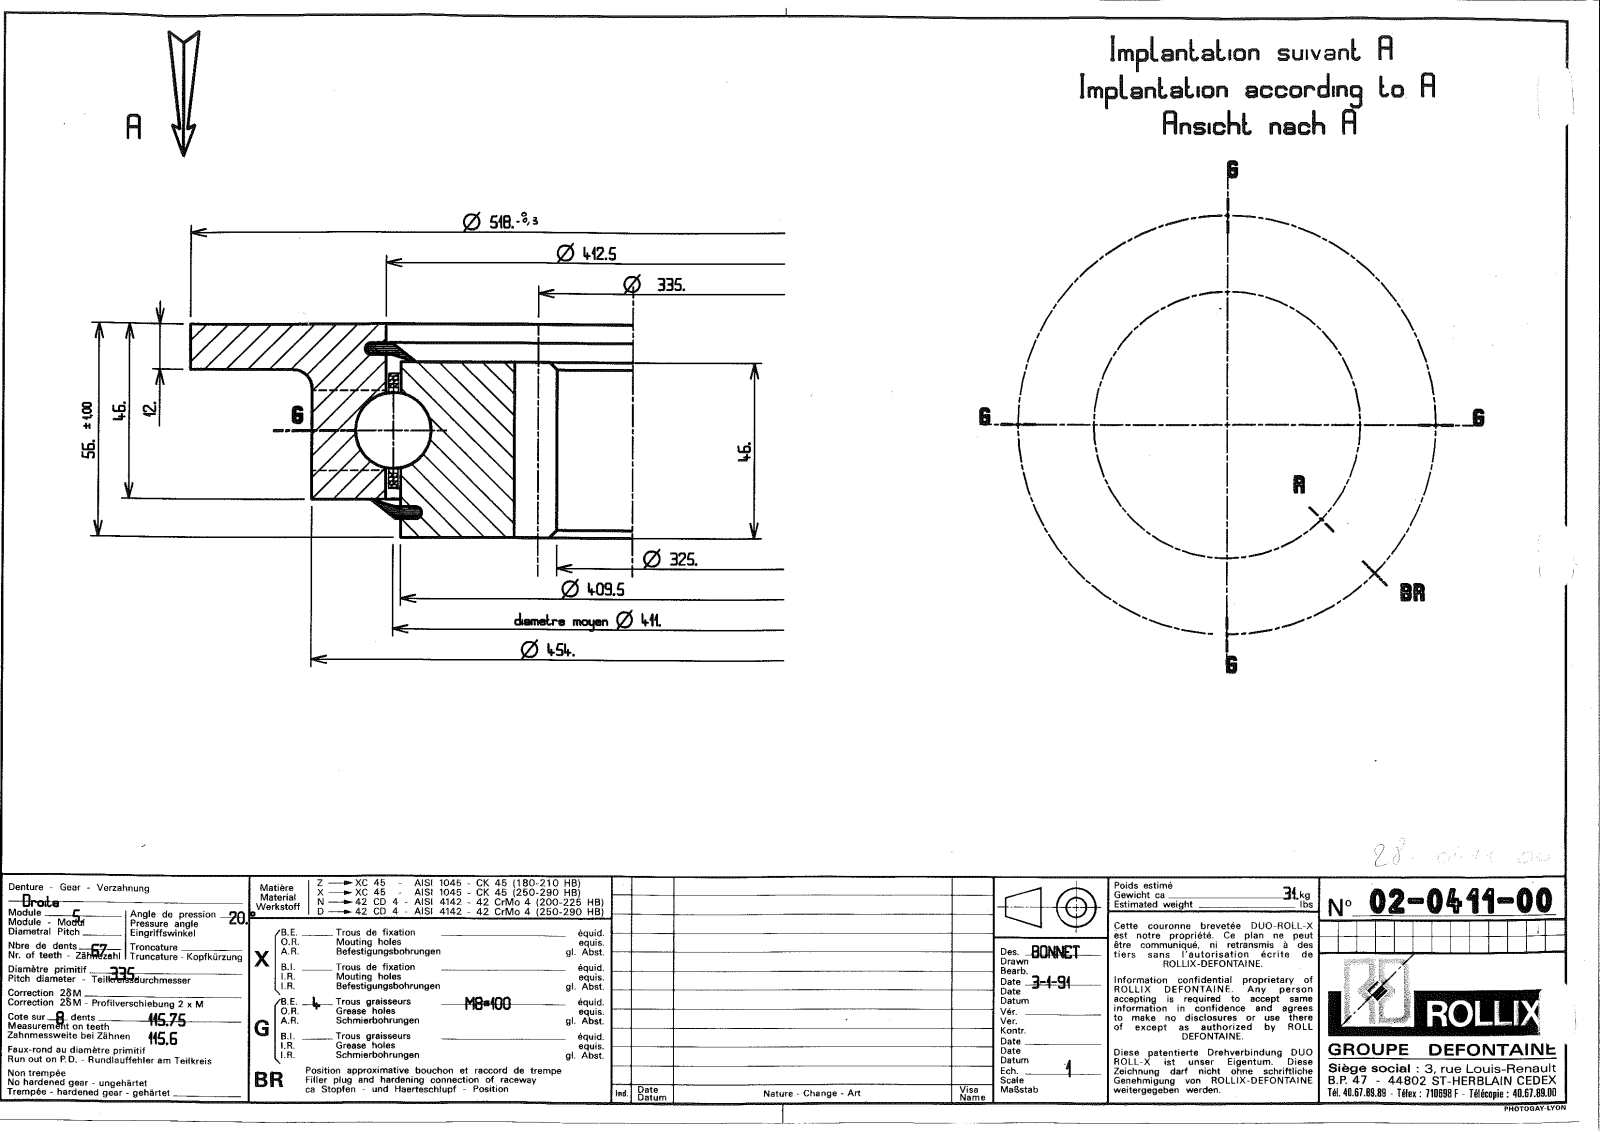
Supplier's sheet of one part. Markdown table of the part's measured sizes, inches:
| quantity | value |
| --- | --- |
| part name | 22-0411-00 |
| STEP written by | SolidWorks 2016 (CONFIG_CONTROL_DESIGN) |
| units | inches |
| bodies | 9 solids, 559 faces (187 planar, 167 cylindrical, 205 other) |
| overall size | 20.394 × 20.394 × 2.205 |
| volume | 211.8 in³ |
| surface area | 981.5 in² |
| round holes (diameter × count) | 0.276 × 4, 16.358 × 1 |
| round bosses / shafts (diameter × count) | 0.315 × 4, 20.394 × 1, 17.874 × 1, 16.004 × 1 |
| partial cylindrical surfaces (radius × count) | 6.398 × 1, 6.841 × 1 |
| main face-to-face distances | 0.394, 1.811, 0.472, 1.732, 2.205, 0.079, 1.339, 1.417, 0.317, 1.888 |
